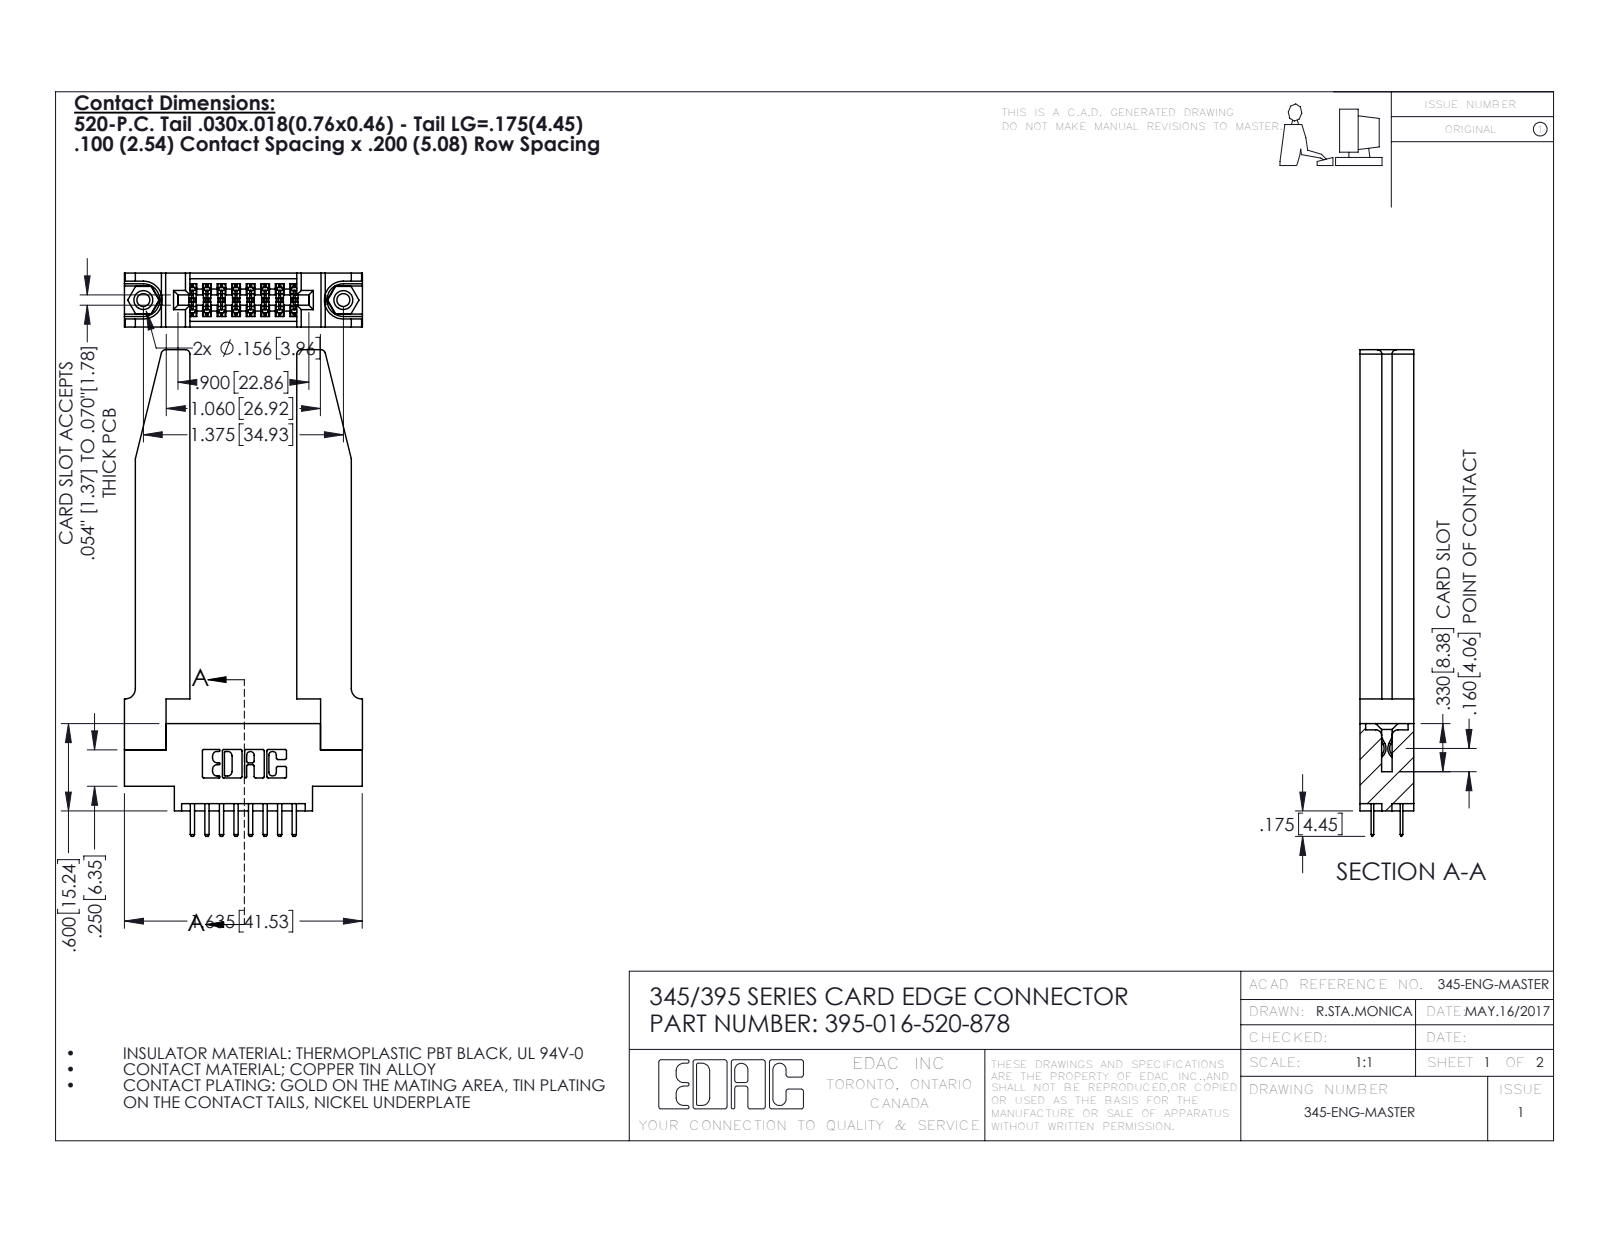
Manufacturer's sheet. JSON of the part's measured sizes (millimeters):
{"part_name": "345-292-001_345-293-120; 395-016-520-878; 345-220-078_345-220-078; 345 Part_0.170 Offset - 0.156 Dia-TH (+1 more)", "step_written_by": "SolidWorks 2016 (CONFIG_CONTROL_DESIGN)", "units": "millimeters", "bodies": {"solids": 21, "faces": 1228, "planar": 786, "cylindrical": 390, "other": 52}, "overall_size": [85, 41.6, 9.4], "volume_mm3": 11400, "surface_area_mm2": 11630, "round_holes": [[2.3, 2], [3.2, 2], [4, 2], [1.6, 1]], "round_bosses_or_shafts": [[3.9, 2]], "partial_cylinders_radius": [[0.2, 24], [0.3, 22], [0.3, 20], [0.8, 8], [0.2, 6], [0.8, 6], [0.7, 3], [0.4, 2]], "face_to_face_distances": [9.4, 1.8, 7.6, 3.8, 5.6, 2, 3.8, 18.7, 2.4, 5.1], "hole_center_spacings": [6.9, 29.1, 34.9]}
